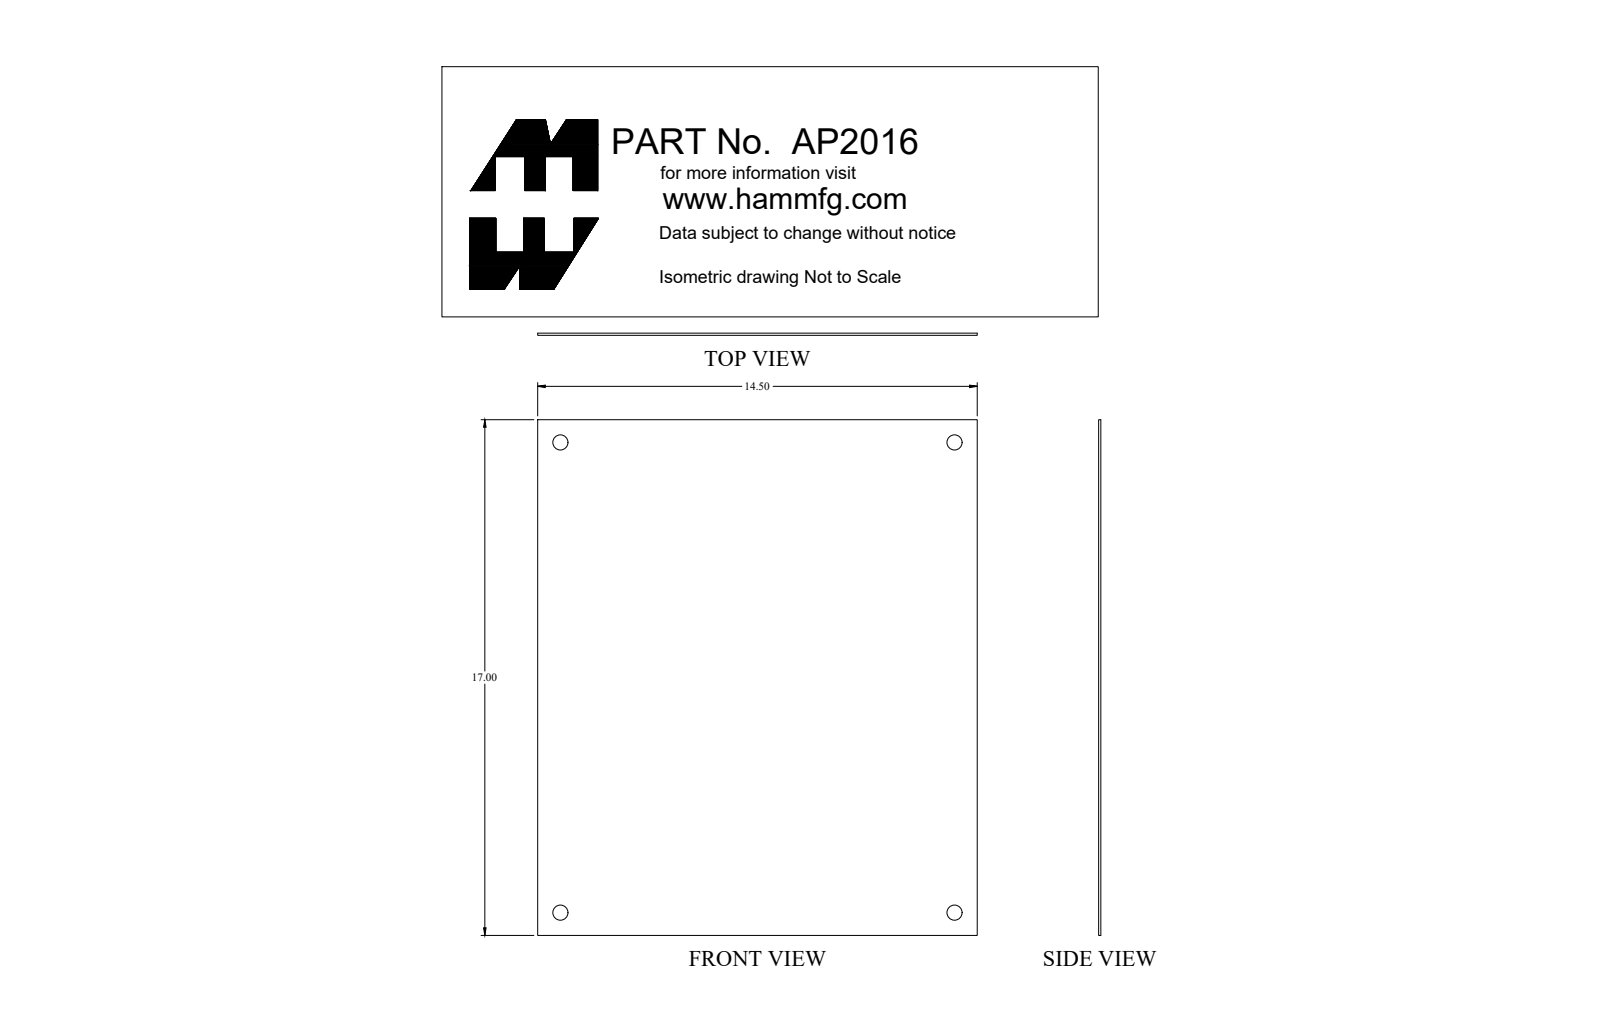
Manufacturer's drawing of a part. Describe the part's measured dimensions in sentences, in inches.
The part is named "AP2016_Default". Its 3-D file was written by "SolidWorks 2019 (CONFIG_CONTROL_DESIGN)". It is 1 solid with 14 faces: 6 planar, 8 cylindrical and 0 other. Overall it measures 17 by 14.5 by 0.072 inches. Its volume is 17.69 cubic inches and its surface area 496.4 square inches. Round holes: 4 of diameter 0.5. The main face-to-face distances are 0.072, 14.5, 17. The hole center spacings are 13, 15.5, 20.23.
